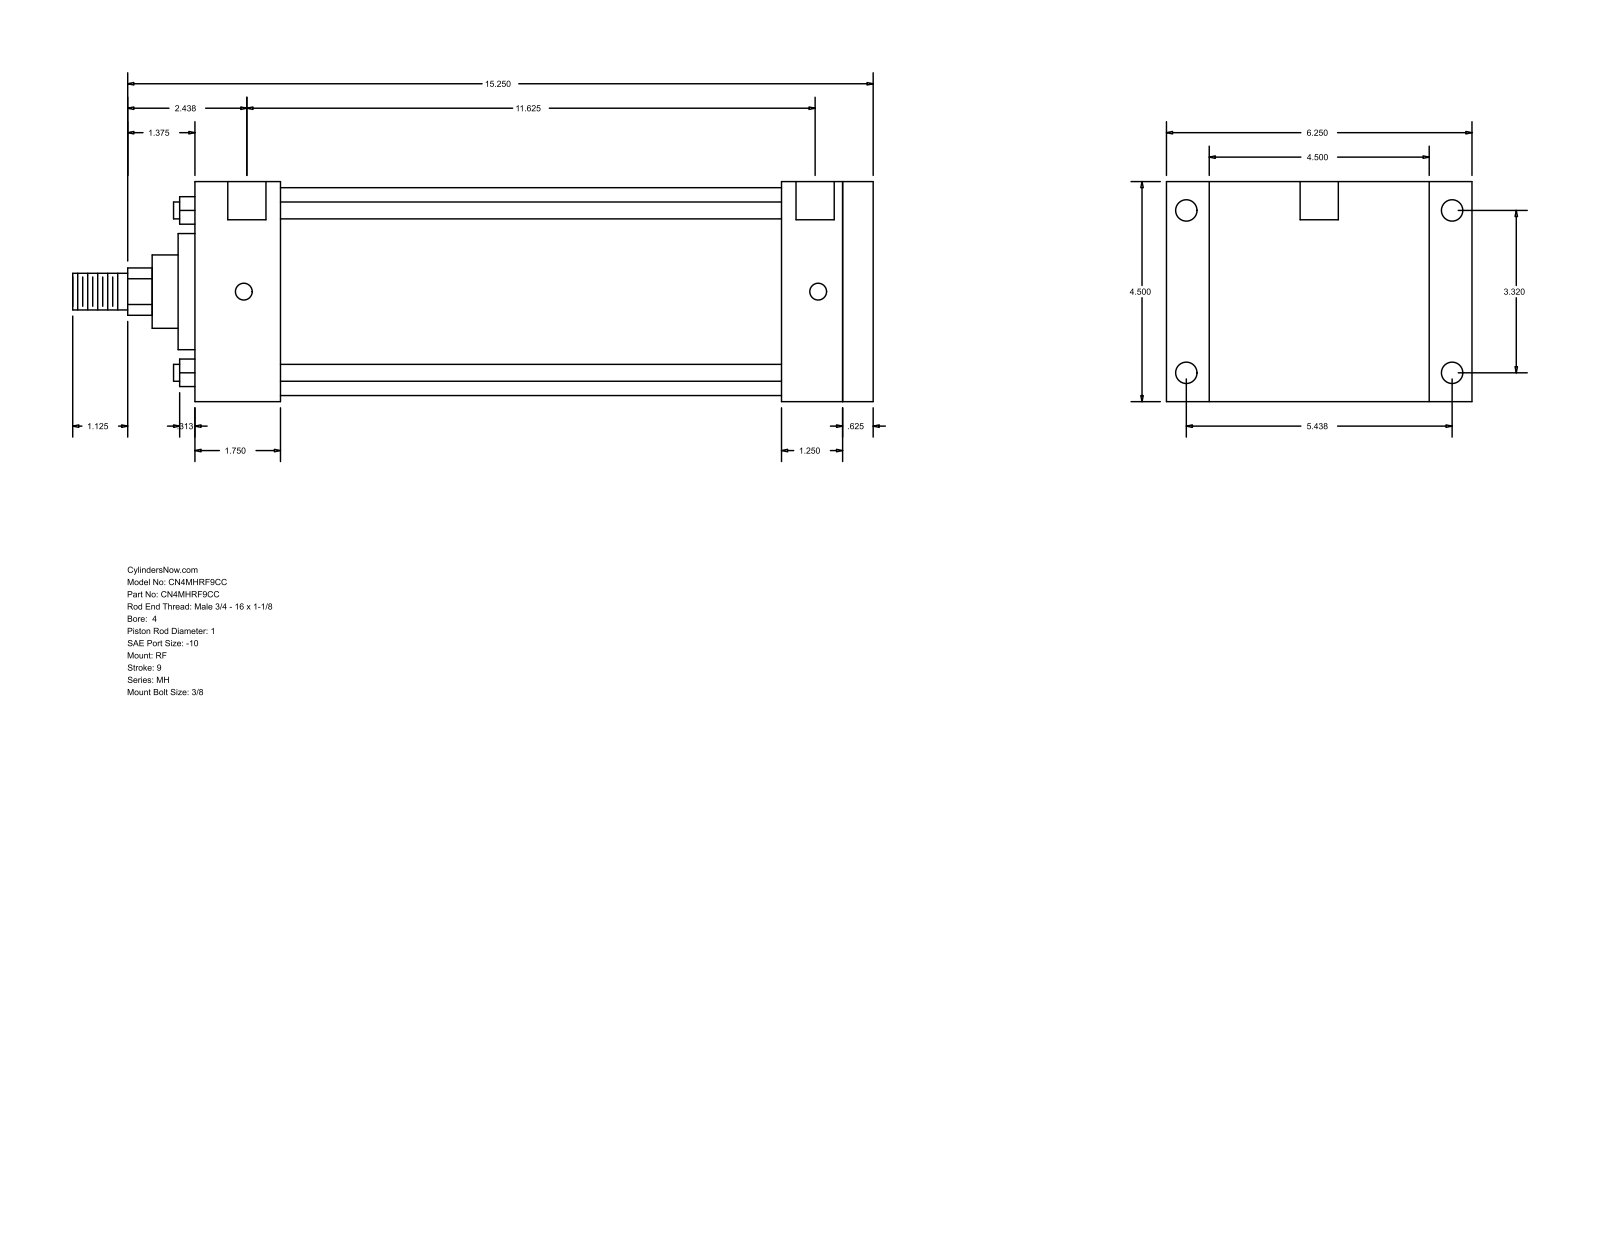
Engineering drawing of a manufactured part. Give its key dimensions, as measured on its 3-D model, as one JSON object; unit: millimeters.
{"part_name": "MH_RF__0400_1", "step_written_by": "GSSL Pune (CONFIG_CONTROL_DESIGN)", "units": "millimeters", "bodies": {"solids": 0, "faces": 94, "planar": 65, "cylindrical": 29, "other": 0}, "overall_size": [415.93, 158.75, 114.3], "round_holes": [[8.73, 4], [11.13, 4], [19.84, 2]], "round_bosses_or_shafts": [[8.76, 4], [107.95, 1], [60.33, 1], [38.1, 1], [25.4, 1], [19.05, 1]], "partial_cylinders_radius": [[12.29, 1]], "face_to_face_distances": [114.3, 352.43, 336.56, 15.87, 44.46, 292.1, 307.97, 304.81, 260.35, 31.75], "hole_center_spacings": [1.58, 84.32, 138.12, 161.82, 296.86, 298.44, 295.28]}
